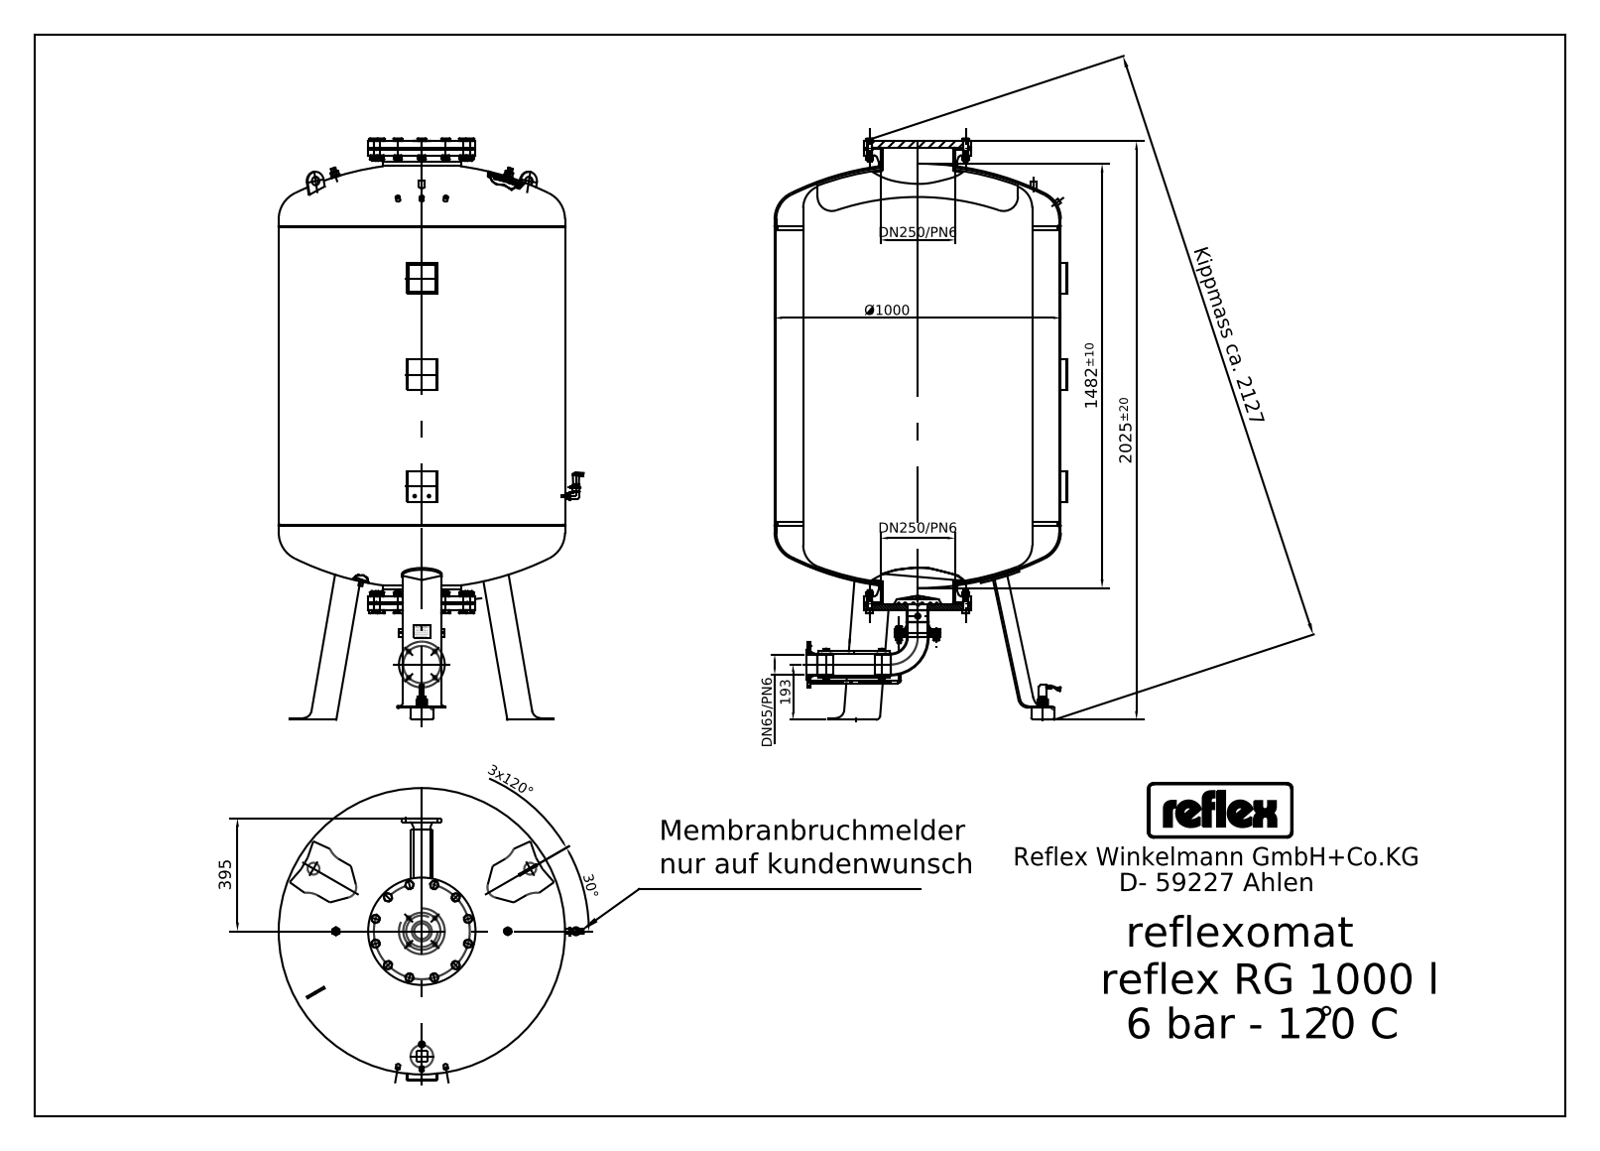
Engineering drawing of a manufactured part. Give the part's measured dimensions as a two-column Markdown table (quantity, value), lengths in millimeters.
| quantity | value |
| --- | --- |
| STEP written by | Mechanical Desktop 2009 (CONFIG_CONTROL_DESIGN) |
| units | millimeters |
| bodies | 33 solids, 1189 faces (675 planar, 280 cylindrical, 234 other) |
| overall size | 2030 × 1066 × 1020 |
| volume | 1 072 000 000 mm³ |
| surface area | 10 900 000 mm² |
| round holes (diameter × count) | 9 × 2, 11.45 × 2, 3.5 × 1, 8 × 1, 14.95 × 1, 30 × 1, 260.4 × 1 |
| round bosses / shafts (diameter × count) | 16 × 12, 12 × 4, 21.3 × 3, 18.5 × 3, 76.1 × 2, 28 × 2, 20 × 2, 10 × 2 |
| partial cylindrical surfaces (radius × count) | 25 × 18, 2 × 10, 1 × 5, 8.44 × 4, 3.38 × 3, 6 × 3, 3 × 2, 5.76 × 2 |
| main face-to-face distances | 1045, 22, 1615, 27, 1588, 1320.5, 275.5, 1342.5, 297.5, 294.5 |
| hole center spacings | 681.46, 50, 395, 519.5, 652.61 |
